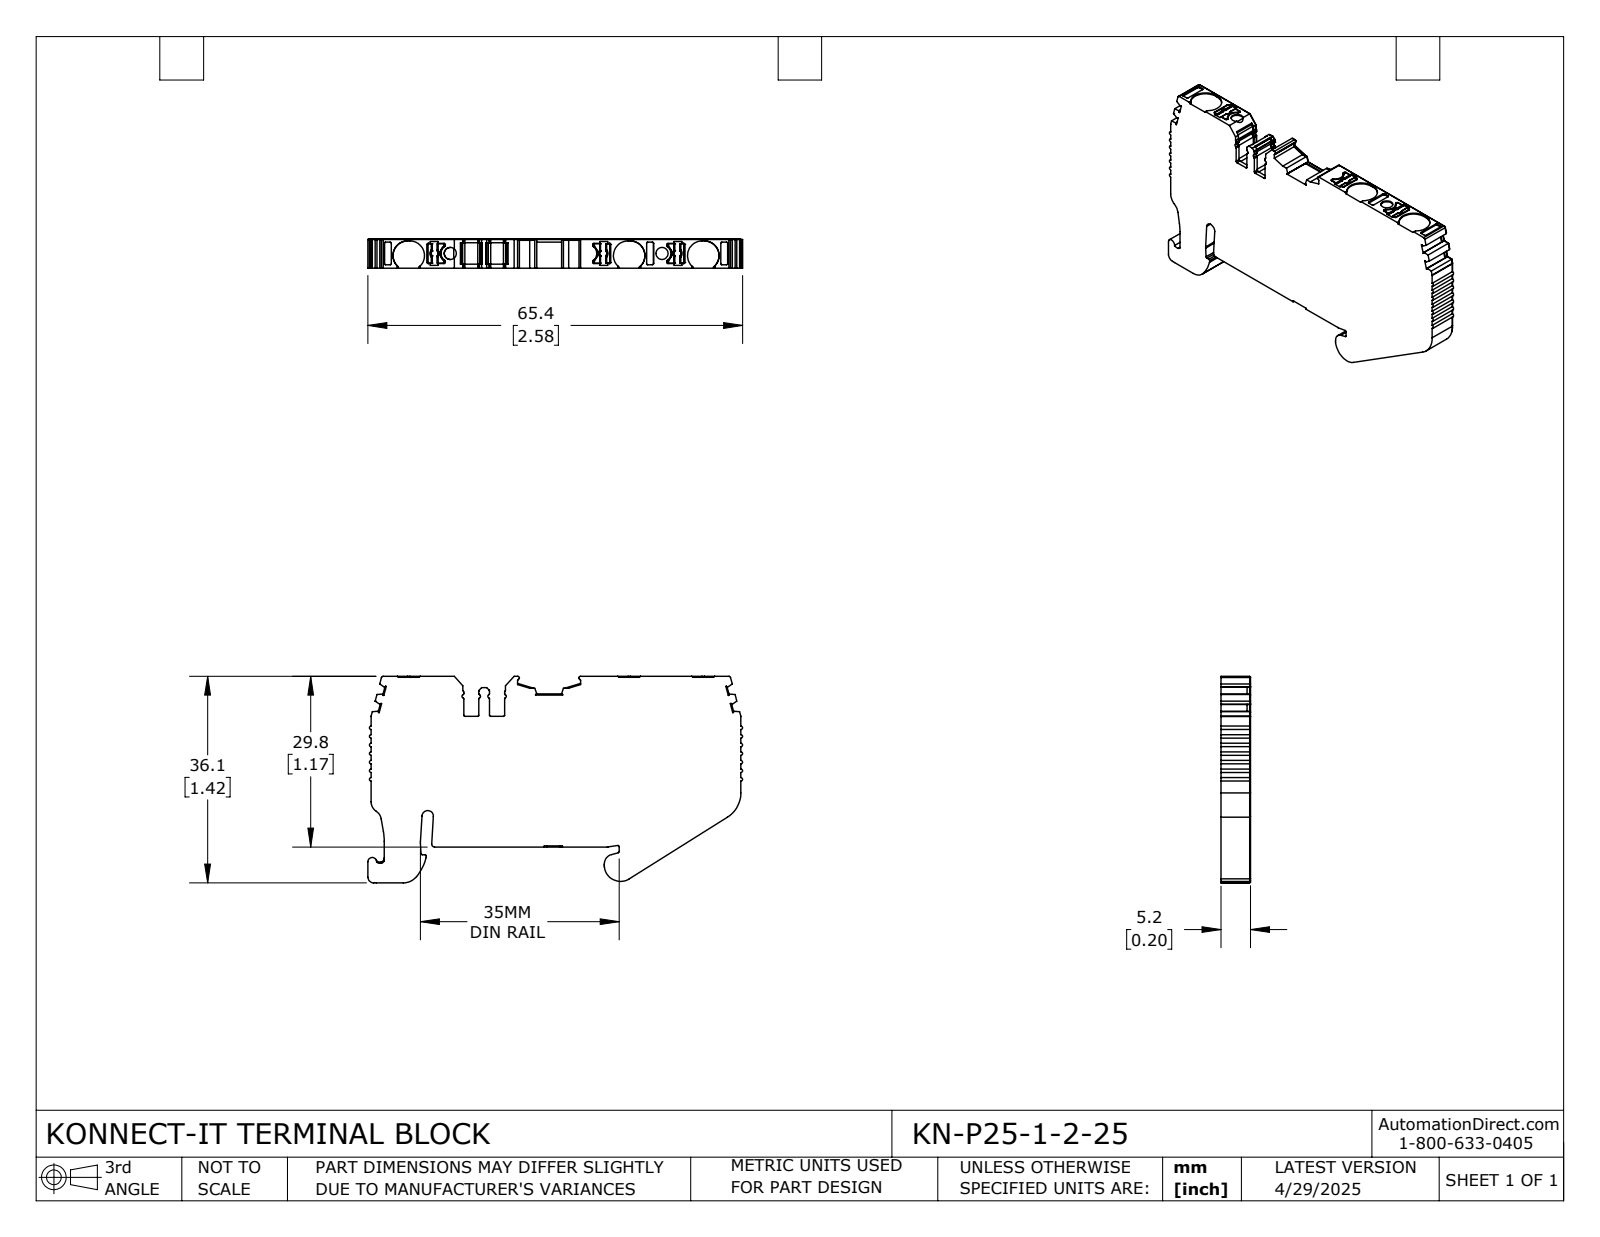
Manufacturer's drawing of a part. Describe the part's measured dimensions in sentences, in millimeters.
The part is named "KN-P25-1-2-25". Its 3-D file was written by "SolidWorks 2024 (CONFIG_CONTROL_DESIGN)". It is 1 solid with 655 faces: 345 planar, 259 cylindrical and 51 other. Overall it measures 65.42 by 36.07 by 5.15 millimeters. Its volume is 9 576 cubic millimeters and its surface area 5 140 square millimeters. Round holes: 2 of diameter 2.1. Partial cylindrical surfaces (rounded edges, fillets, slot ends): 66 of radius 0.2, 39 of radius 0.3, 19 of radius 0.1, 18 of radius 0.5, 12 of radius 0.15, 9 of radius 0.4, 6 of radius 2.55, 3 of radius 1. The main face-to-face distances are 5.15, 29.61, 29.81, 64.58, 4.5, 5, 6.26, 35.87, 2, 36.07. The hole center spacings are 36.98.
